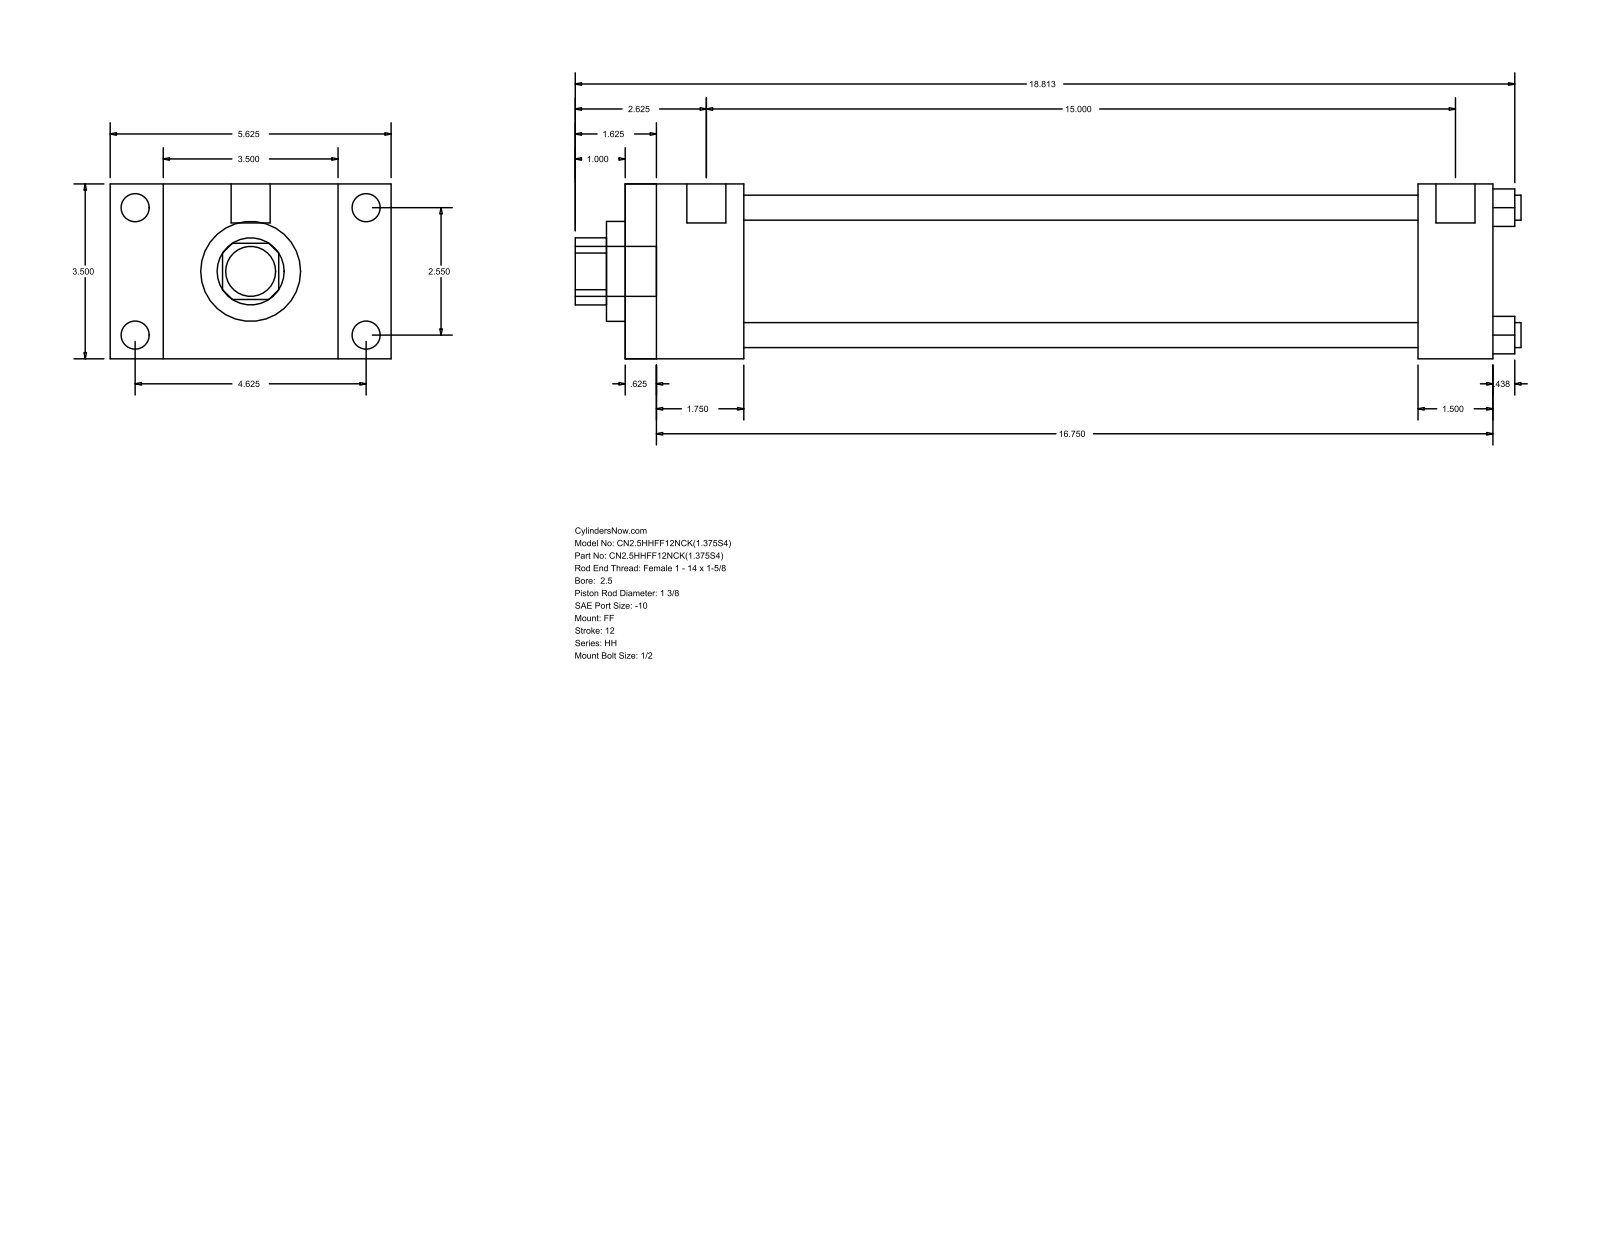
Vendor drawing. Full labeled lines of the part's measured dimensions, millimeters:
Part name (STEP PRODUCT): HH_FF__0250_1.375
STEP written by: GSSL Pune (CONFIG_CONTROL_DESIGN)
Units: millimetres
Bodies: 0 solids, 92 faces (64 planar, 28 cylindrical, 0 other)
Overall size (bounding box): 481.01 × 142.88 × 88.9
Round holes (diameter × count): ⌀12.7 ×4, ⌀34.92 ×1, ⌀50.8 ×1, ⌀73.03 ×1
Round bosses / shafts (diameter × count): ⌀14.3 ×4, ⌀5.56 ×4, ⌀19.84 ×2, ⌀25.4 ×1
Partial cylindrical surfaces — rounded edges, fillets, slot ends (radius × count): R17.06 ×1
Main face-to-face distances: 88.9, 441.33, 15.87, 425.46, 60.32, 44.45, 381.01, 403.22, 387.35, 342.9
Hole centre spacings: 45.79, 64.76, 91.58
